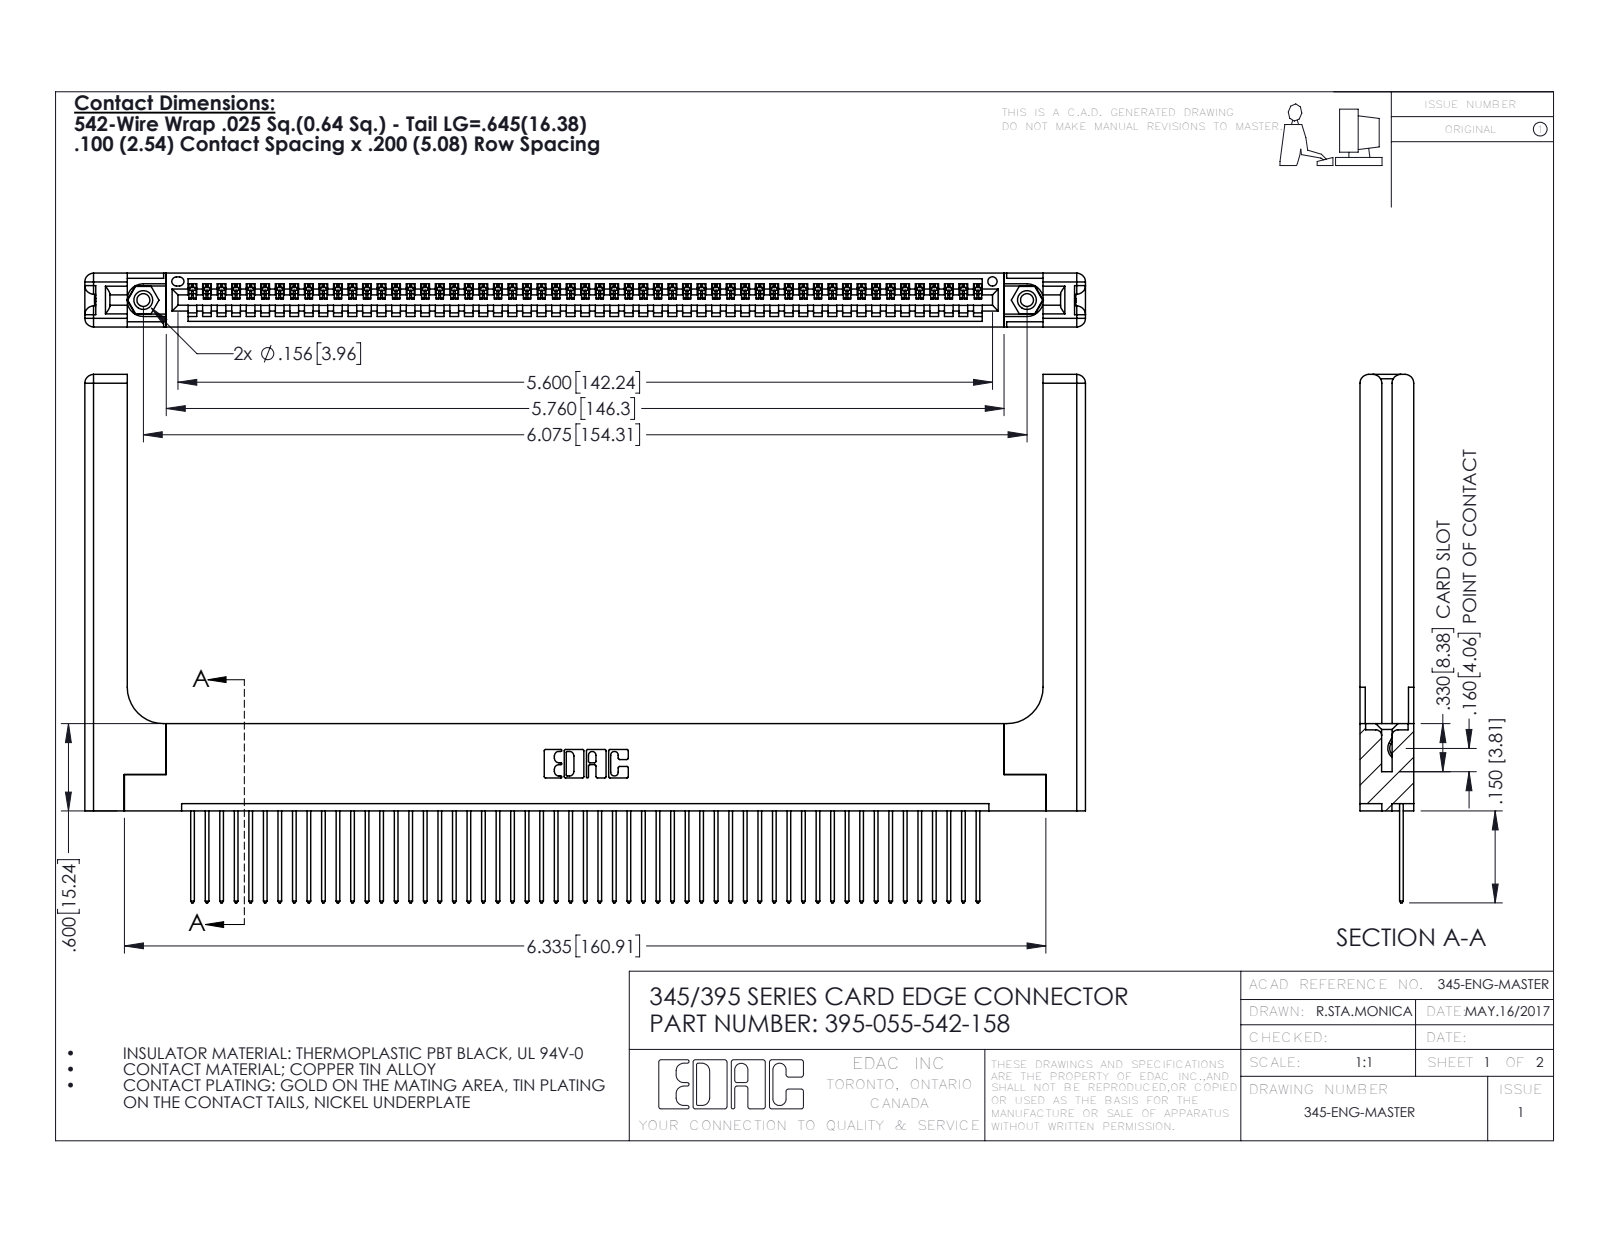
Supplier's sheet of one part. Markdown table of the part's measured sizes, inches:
| quantity | value |
| --- | --- |
| part name | 345-220-058_345-220-058; 345-292-001_345-293-142; 345 Part_Flush Mounting Lugs - 0.156 Dia-TH; 395-055-542-158 (+1 more) |
| STEP written by | SolidWorks 2016 (CONFIG_CONTROL_DESIGN) |
| units | inches |
| bodies | 60 solids, 3572 faces (2428 planar, 1084 cylindrical, 60 other) |
| overall size | 6.879 × 3.632 × 0.37 |
| volume | 1.546 in³ |
| surface area | 44.35 in² |
| round holes (diameter × count) | 0.089 × 2, 0.125 × 2, 0.156 × 2, 0.064 × 1 |
| round bosses / shafts (diameter × count) | 0.155 × 2 |
| partial cylindrical surfaces (radius × count) | 0.006 × 110, 0.01 × 110, 0.01 × 22, 0.06 × 16, 0.007 × 6, 0.031 × 6, 0.026 × 3, 0.03 × 2 |
| main face-to-face distances | 0.072, 0.298, 0.37, 0.098, 0.272, 0.025, 0.2, 0.225, 0.148, 0.15 |
| hole center spacings | 0.27, 5.839, 6.075 |
